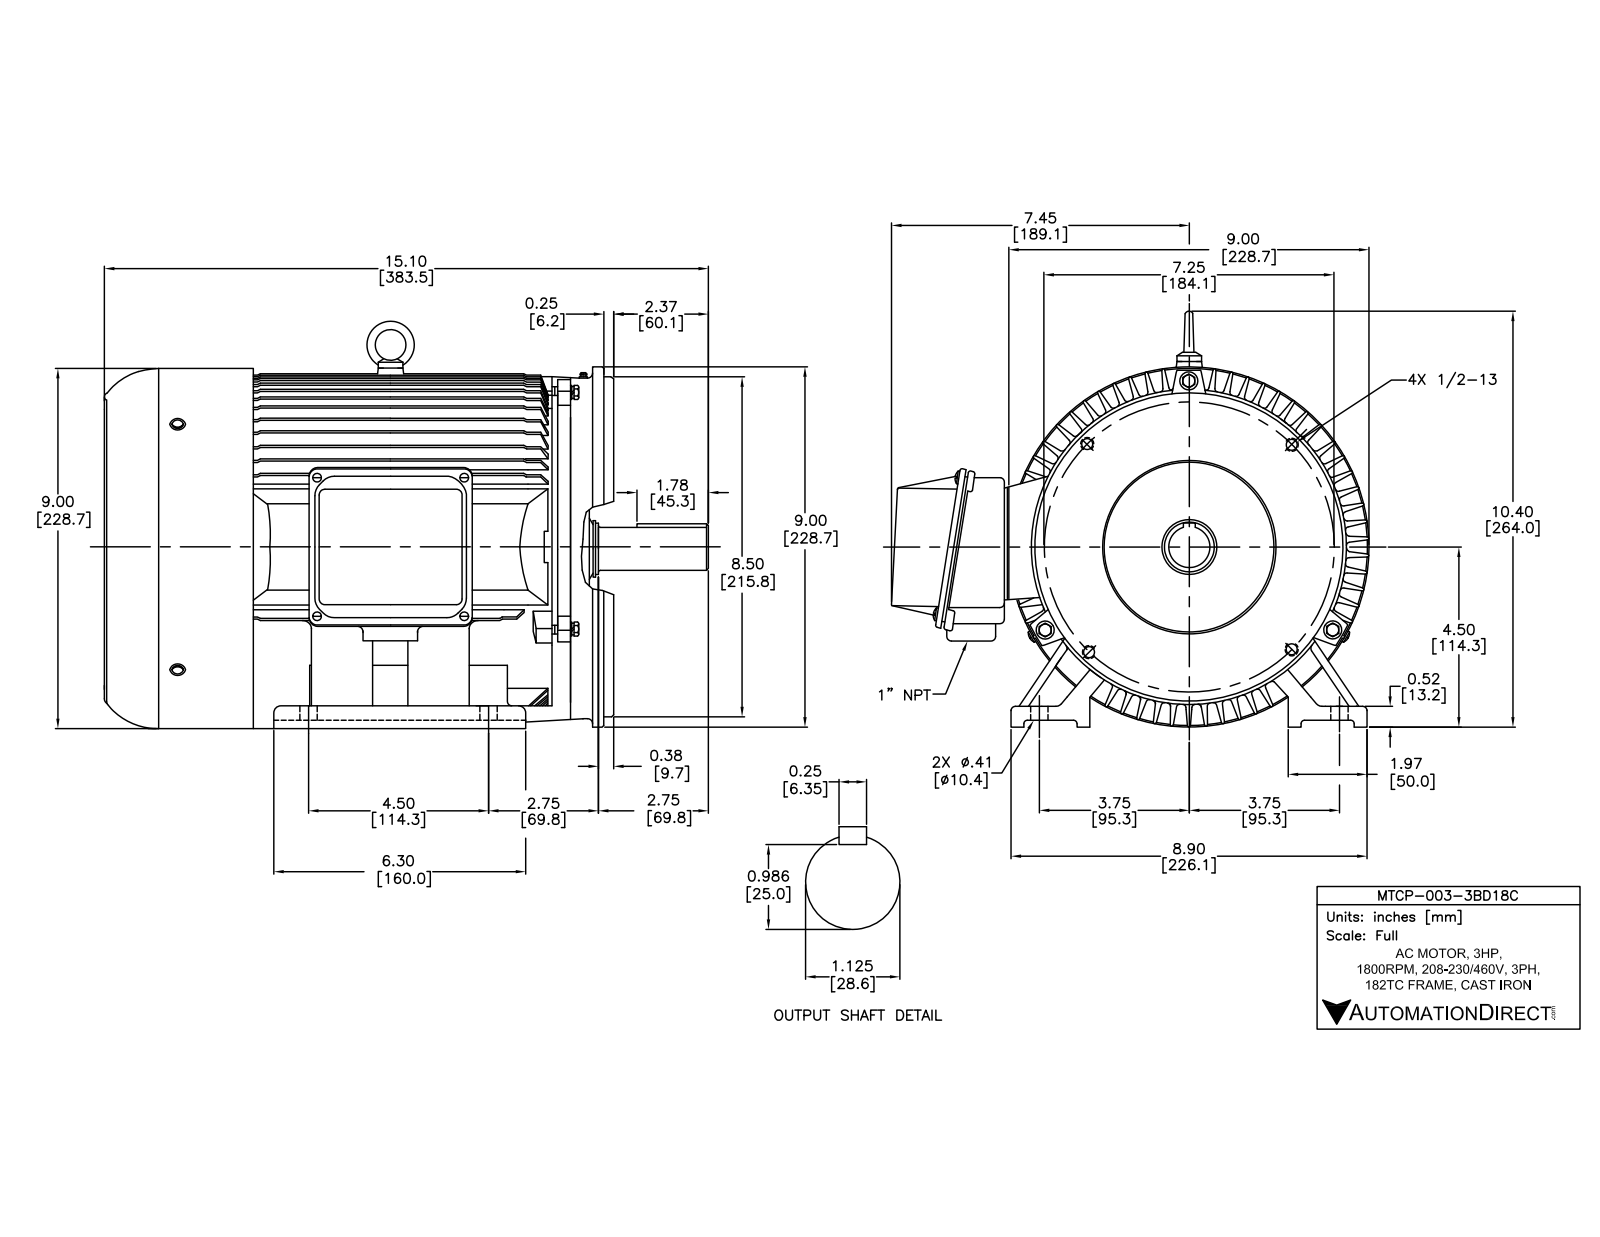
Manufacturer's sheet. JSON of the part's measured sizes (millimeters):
{"part_name": "MTCP182TC; spring lock washers--normal type gb_GB_FASTENER_WASHER_SW 5; PE180接线盒座_默认_按加工; spring lock washers--normal type gb_GB_FASTENER_WASHER_SW 8 (+6 more)", "step_written_by": "SolidWorks 2017 (AUTOMOTIVE_DESIGN)", "units": "millimeters", "bodies": {"solids": 47, "faces": 2531, "planar": 694, "cylindrical": 939, "other": 898}, "overall_size": [385.6, 301.42, 265.4], "volume_mm3": 3024000, "surface_area_mm2": 997448, "round_holes": [[5.8, 15], [4.2, 11], [6.8, 4], [7.94, 4], [10.5, 4], [10.72, 4], [5.3, 3], [5.4, 3], [8.4, 3], [8.68, 3], [10, 3], [22, 3]], "round_bosses_or_shafts": [[5, 11], [8, 7], [16, 3], [12.88, 3], [10, 3], [226, 1], [219.4, 1], [215.9, 1]], "partial_cylinders_radius": [[1, 182], [0.5, 67], [2, 59], [3, 35], [1.25, 33], [7, 22], [0.34, 16], [8, 11]], "face_to_face_distances": [5, 6, 1.2, 241.2, 278.6, 277.4, 7, 314.8, 313.6, 36.2], "hole_center_spacings": [68, 118.52, 100, 17.47, 68.01, 74.61, 92.08, 96.17]}
